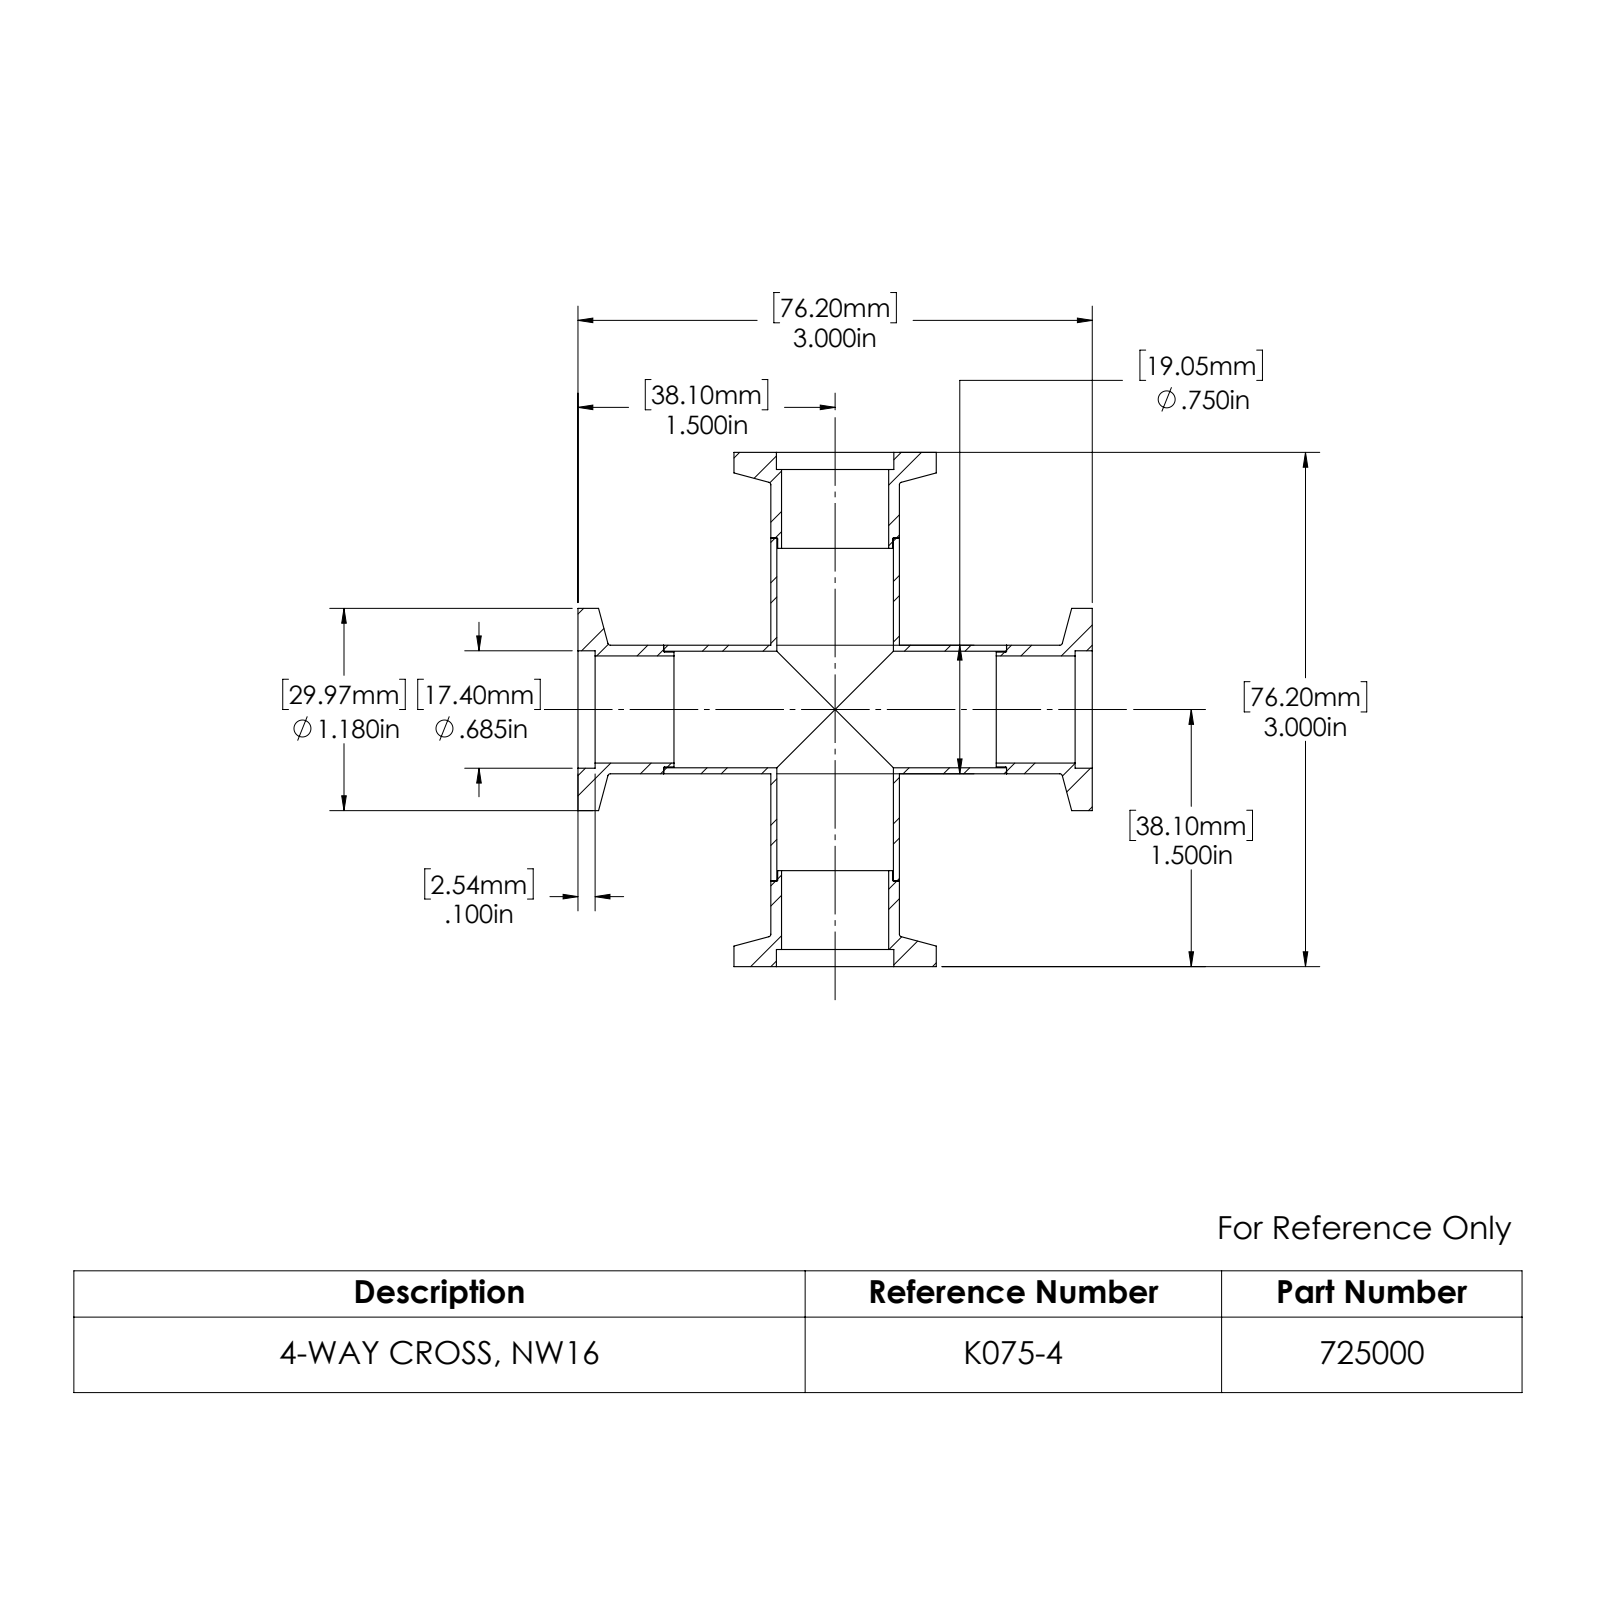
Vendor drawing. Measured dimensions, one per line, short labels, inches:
name: 713001; 940500; 725000
written by: SolidWorks 2022 (AUTOMOTIVE_DESIGN)
unit: in
bodies: 5 solids, 100 faces (20 planar, 56 cylindrical, 24 other)
size: 3 × 3 × 1.18
volume: 0.882 in³; area: 30.32 in²
holes: 2× ⌀0.625, 2× ⌀0.68, 2× ⌀0.685
bosses: 2× ⌀1.18, 2× ⌀0.75, 2× ⌀0.67
face distances: 3, 0.5, 2.5, 2, 0.1, 2.9, 0.4, 2.4, 0.56, 2.44
